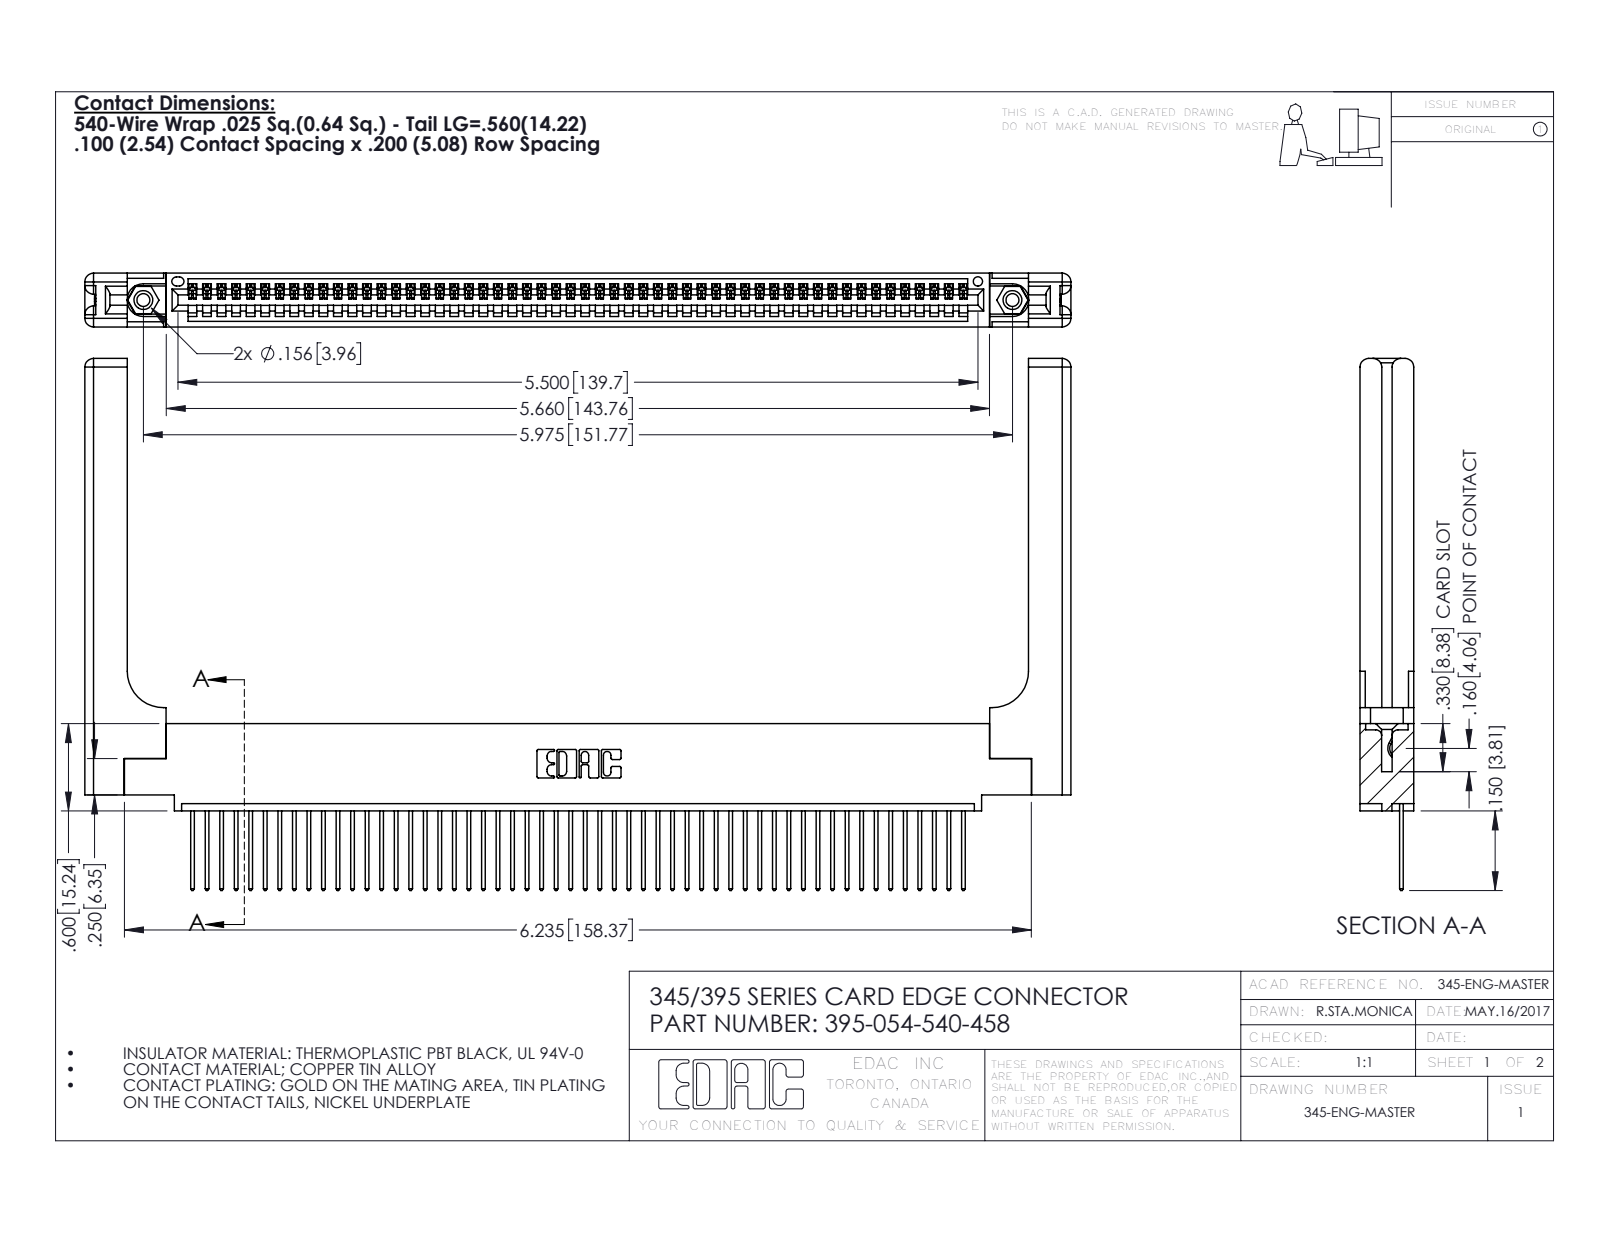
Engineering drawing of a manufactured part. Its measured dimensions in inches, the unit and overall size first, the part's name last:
Units: inches
Overall size (bounding box): 6.779 × 3.657 × 0.37
Round holes (diameter × count): ⌀0.089 ×2, ⌀0.125 ×2, ⌀0.156 ×2, ⌀0.064 ×1
Round bosses / shafts (diameter × count): ⌀0.155 ×2
Partial cylindrical surfaces — rounded edges, fillets, slot ends (radius × count): R0.006 ×108, R0.01 ×108, R0.01 ×22, R0.06 ×16, R0.007 ×6, R0.031 ×6, R0.026 ×3, R0.03 ×2
Main face-to-face distances: 0.072, 0.298, 0.37, 0.098, 0.272, 0.025, 0.2, 0.225, 0.148, 0.15
Hole centre spacings: 0.27, 5.739, 5.975
Volume: 1.523 in³ · Surface area: 43.31 in²
Bodies: 59 solids, 3518 faces (2392 planar, 1066 cylindrical, 60 other)
Part name (STEP PRODUCT): 395-054-540-458; 345-250-001_345-250-001-102; 345-292-001_345-293-140; 345-220-058_345-220-058 (+1 more)
STEP written by: SolidWorks 2016 (CONFIG_CONTROL_DESIGN)
